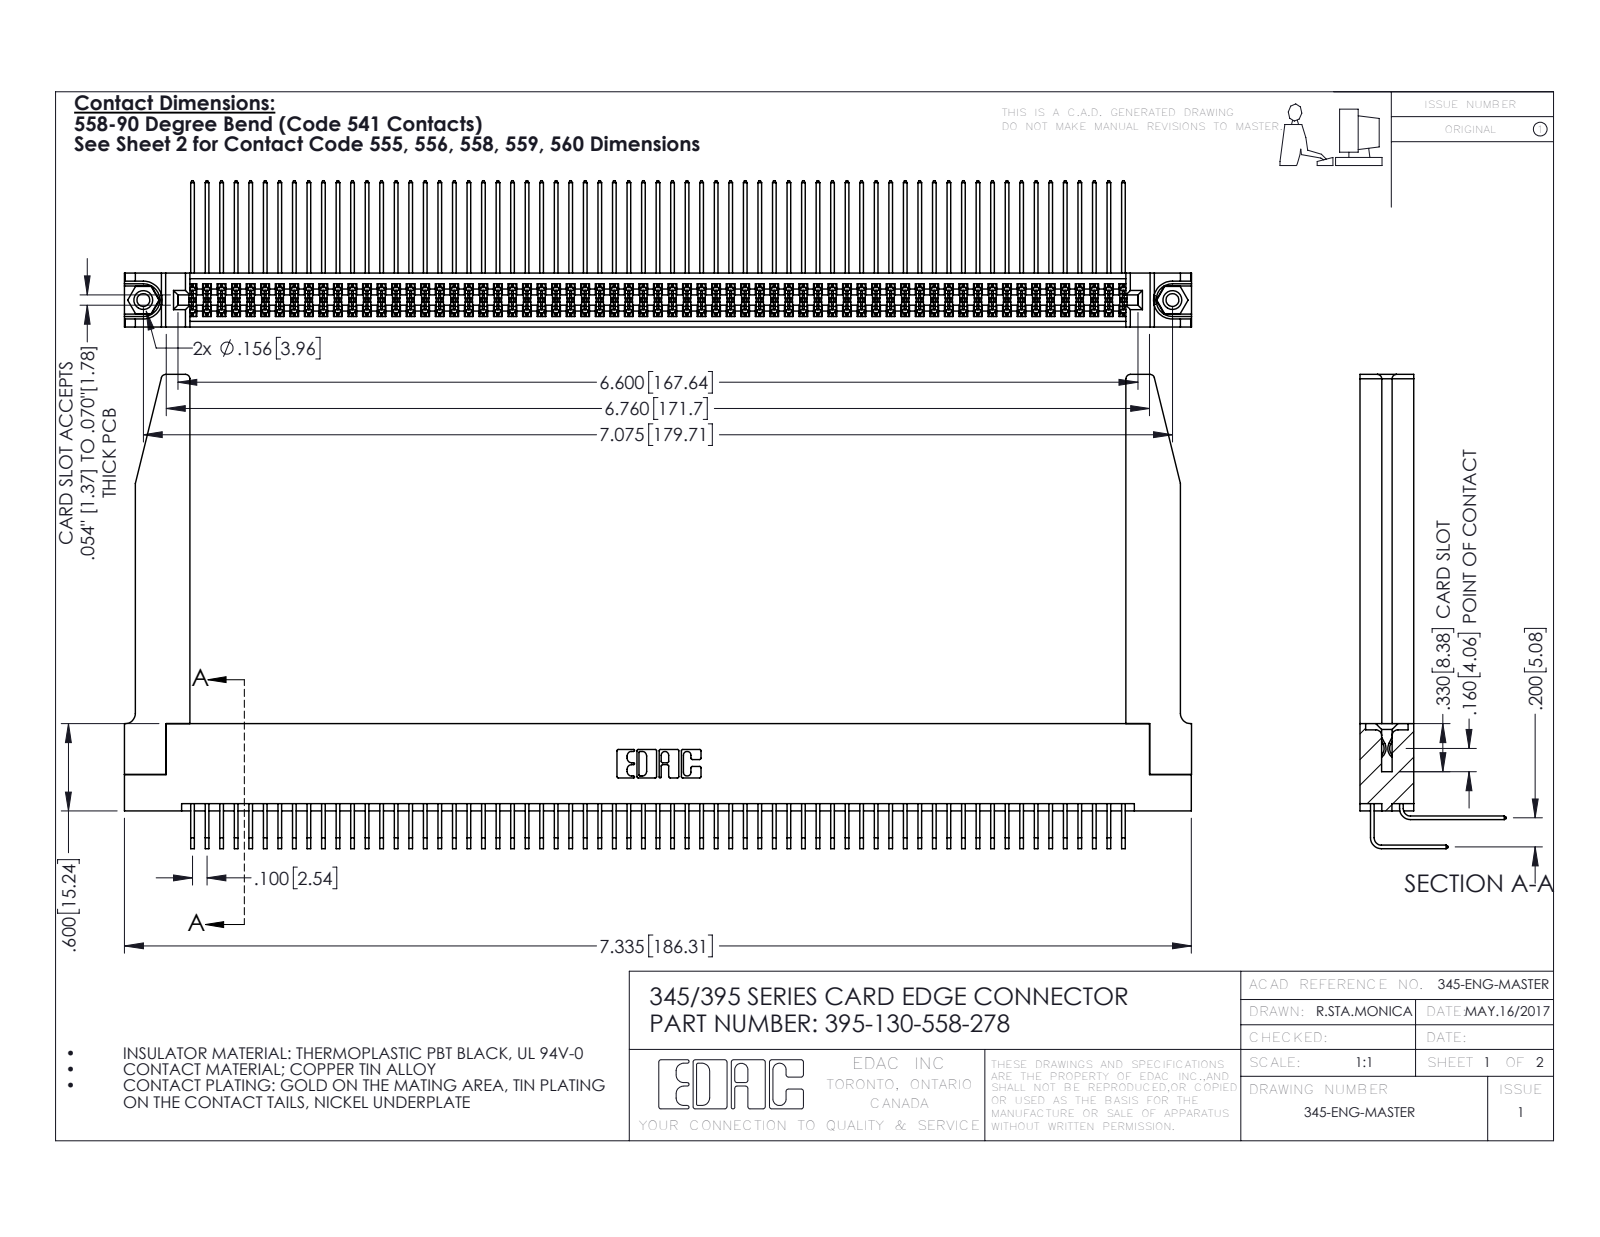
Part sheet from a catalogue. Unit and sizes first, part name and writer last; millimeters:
Units: millimetres
Overall size (bounding box): 186.3 × 82.8 × 25.5
Round holes (diameter × count): ⌀2.3 ×2, ⌀3.2 ×2, ⌀4 ×2, ⌀1.6 ×1
Round bosses / shafts (diameter × count): ⌀3.9 ×2
Partial cylindrical surfaces — rounded edges, fillets, slot ends (radius × count): R0.2 ×195, R0.3 ×22, R0.8 ×8, R0.2 ×6, R0.8 ×6, R0.7 ×3, R0.4 ×2, R0.5 ×2
Main face-to-face distances: 1.8, 7.6, 9.4, 5.1, 2.5, 6.9, 0.6, 5.7, 0.6, 7.2
Hole centre spacings: 6.9, 173.7, 179.7
Volume: 26 840 mm³ · Surface area: 38 990 mm²
Bodies: 135 solids, 7120 faces (4772 planar, 2296 cylindrical, 52 other)
Part name (STEP PRODUCT): 395-130-558-278; 345-250-001_345-250-001-102; 345-292-001_558 Tail - 2; 345 Part_Flush Mounting Lugs - 0.156 Dia-TH (+2 more)
STEP written by: SolidWorks 2016 (CONFIG_CONTROL_DESIGN)
